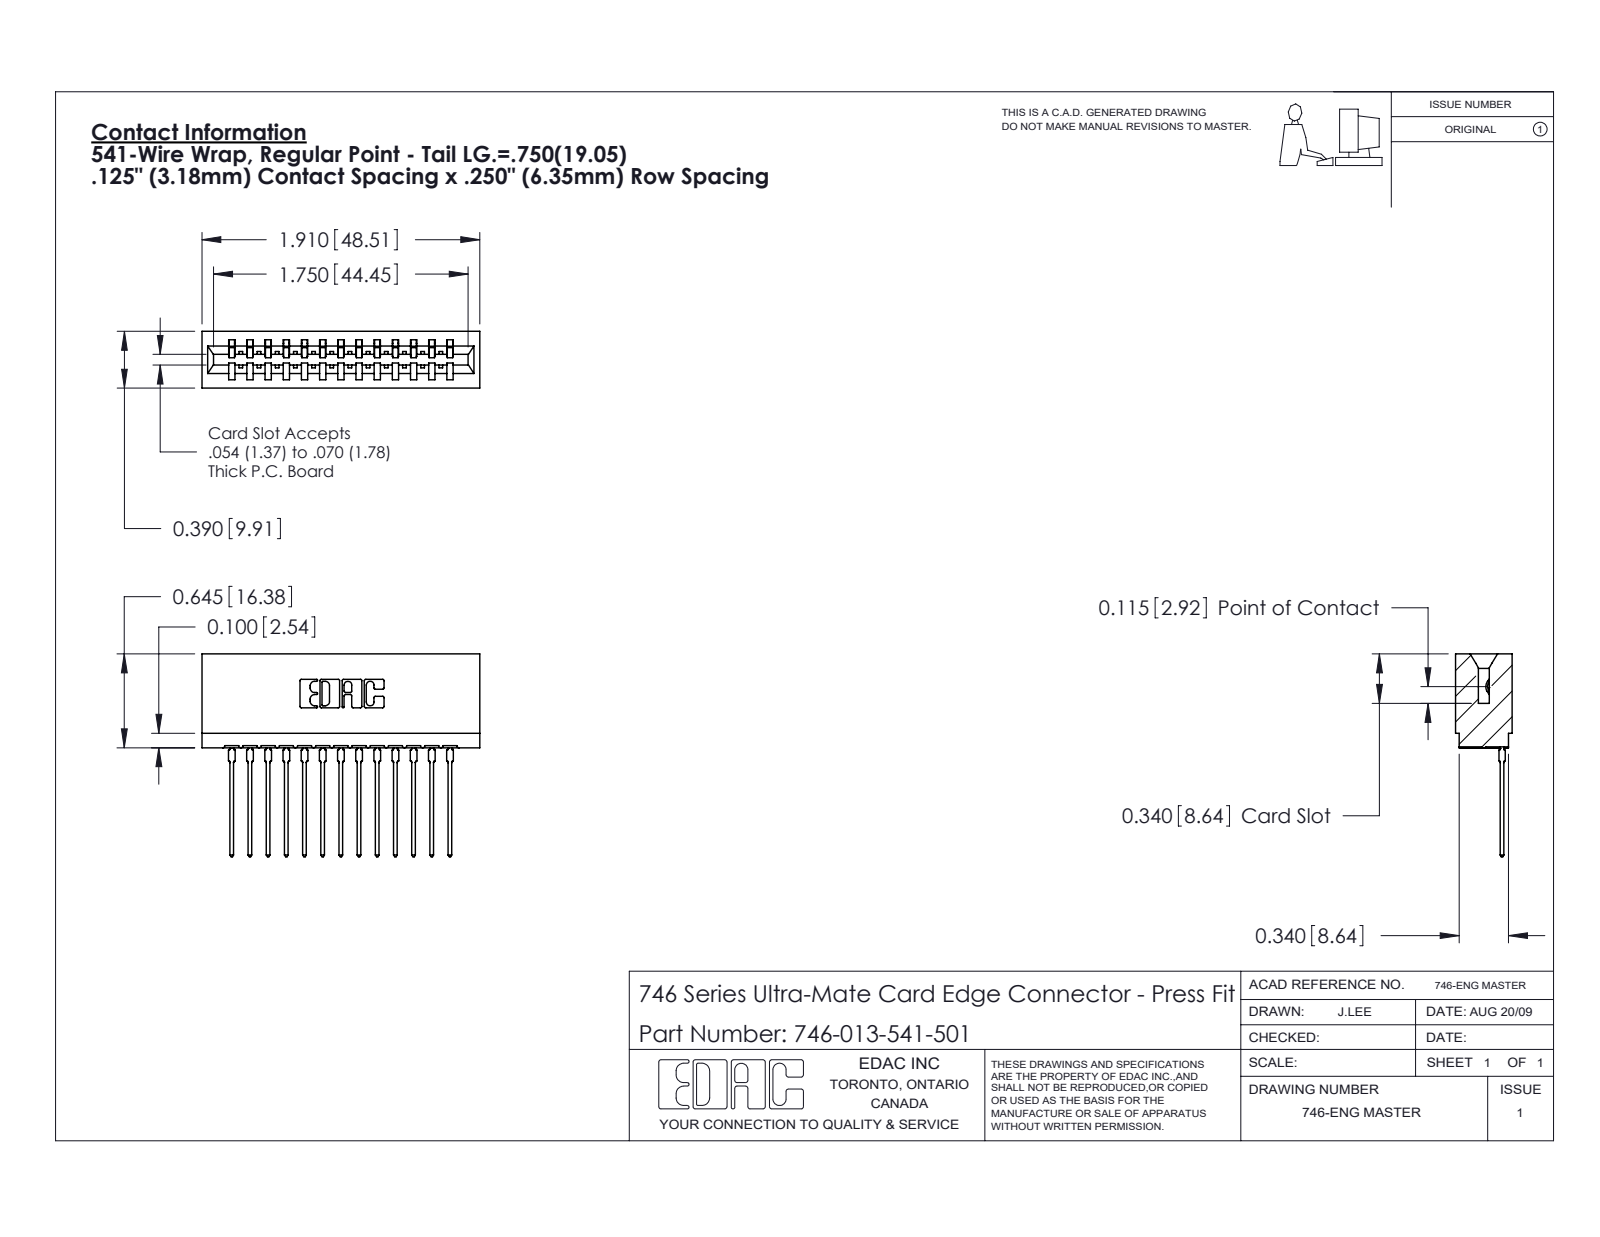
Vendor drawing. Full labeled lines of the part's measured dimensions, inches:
Part name (STEP PRODUCT): 746-292-001_541; 746-013-541-501; 746 Part_.340 Slot Depth - 01
STEP written by: SolidWorks 2020 (CONFIG_CONTROL_DESIGN)
Units: inches
Bodies: 14 solids, 1501 faces (874 planar, 289 cylindrical, 338 other)
Overall size (bounding box): 1.91 × 1.394 × 0.39
Volume: 0.347 in³ · Surface area: 11.69 in²
Partial cylindrical surfaces — rounded edges, fillets, slot ends (radius × count): R0.021 ×26, R0.01 ×22, R0.015 ×14, R0.007 ×6, R0.031 ×6, R0.005 ×4, R0.011 ×4, R0.026 ×3
Main face-to-face distances: 0.25, 0.333, 0.057, 0.5, 0.125, 0.39, 0.042, 0.292, 0.75, 0.125
